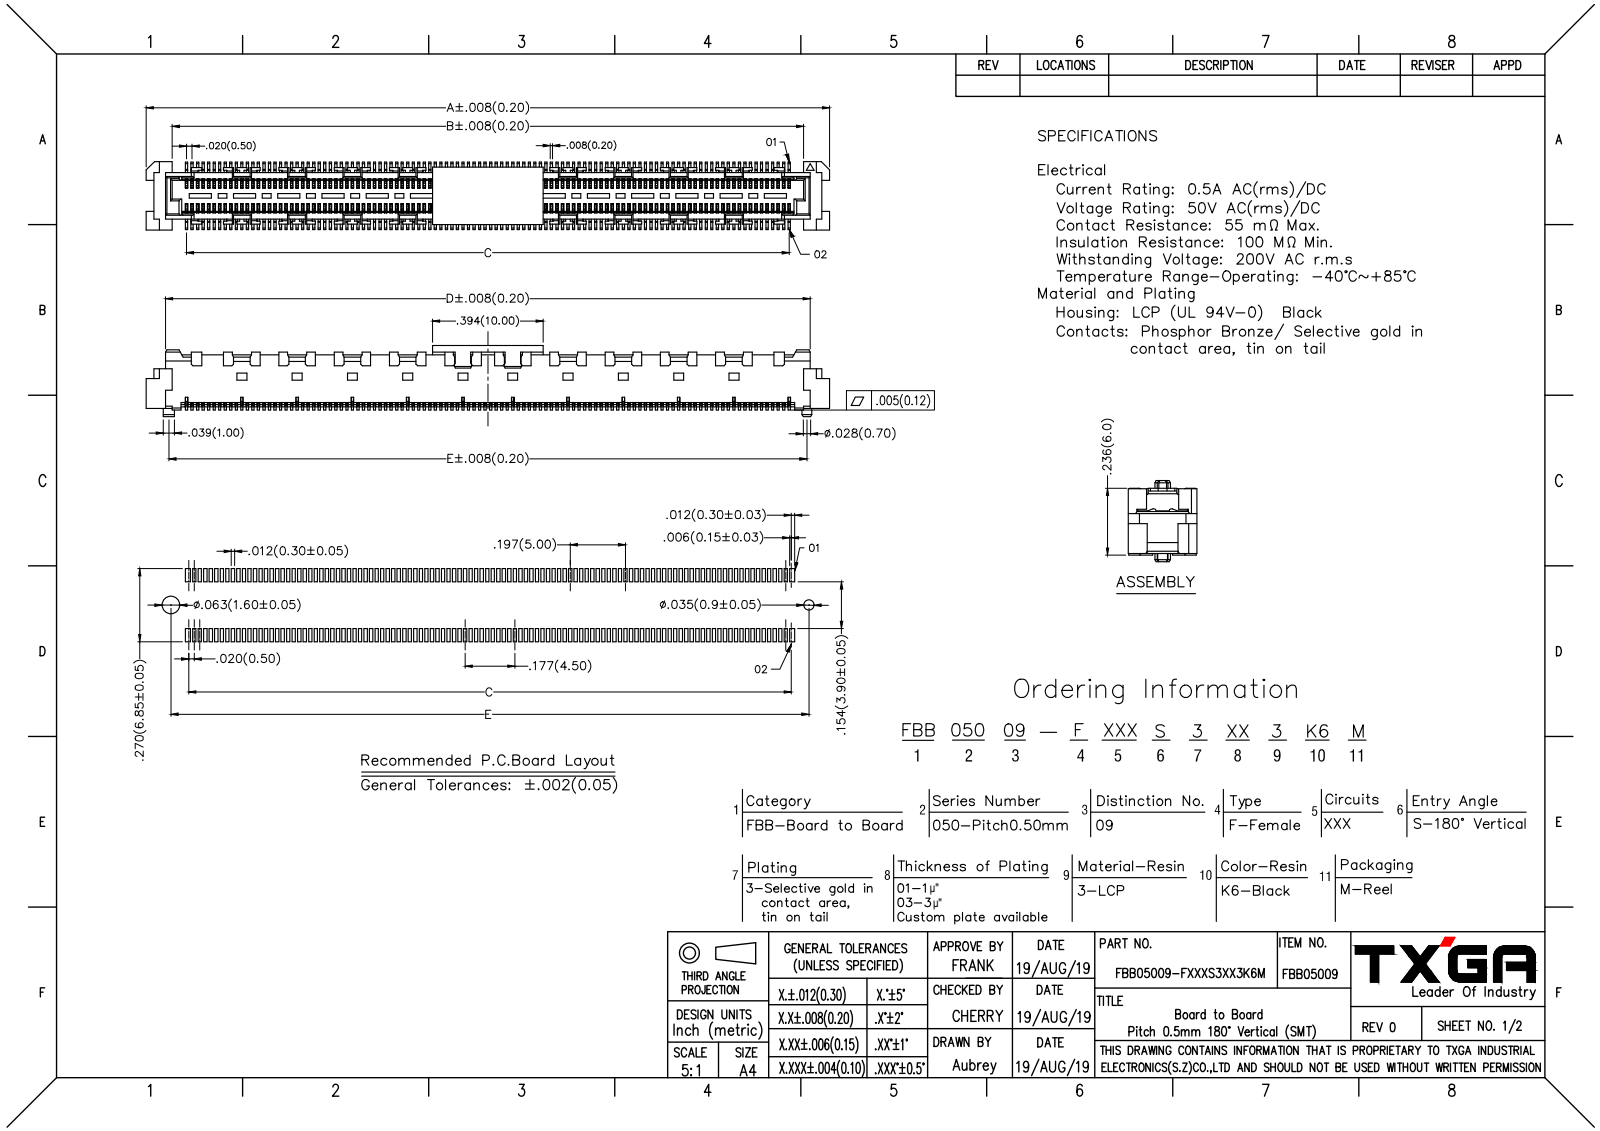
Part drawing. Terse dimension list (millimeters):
name: PRT0002
written by: PRO/ENGINEER BY PARAMETRIC TECHNOLOGY CORPORATION, 2008380 (CONFIG_CONTROL_DESIGN)
unit: mm
bodies: 1 solid, 2066 faces (1842 planar, 224 cylindrical, 0 other)
size: 61.8 × 6.2 × 6
volume: 853 mm³; area: 2 082 mm²
bosses: 1× ⌀0.7
rounds: 2× R1, 1× R0.7
face distances: 3.5, 0.8, 4.3, 2.15, 2.7, 0.5, 2.35, 2.4, 4.5, 2.65
